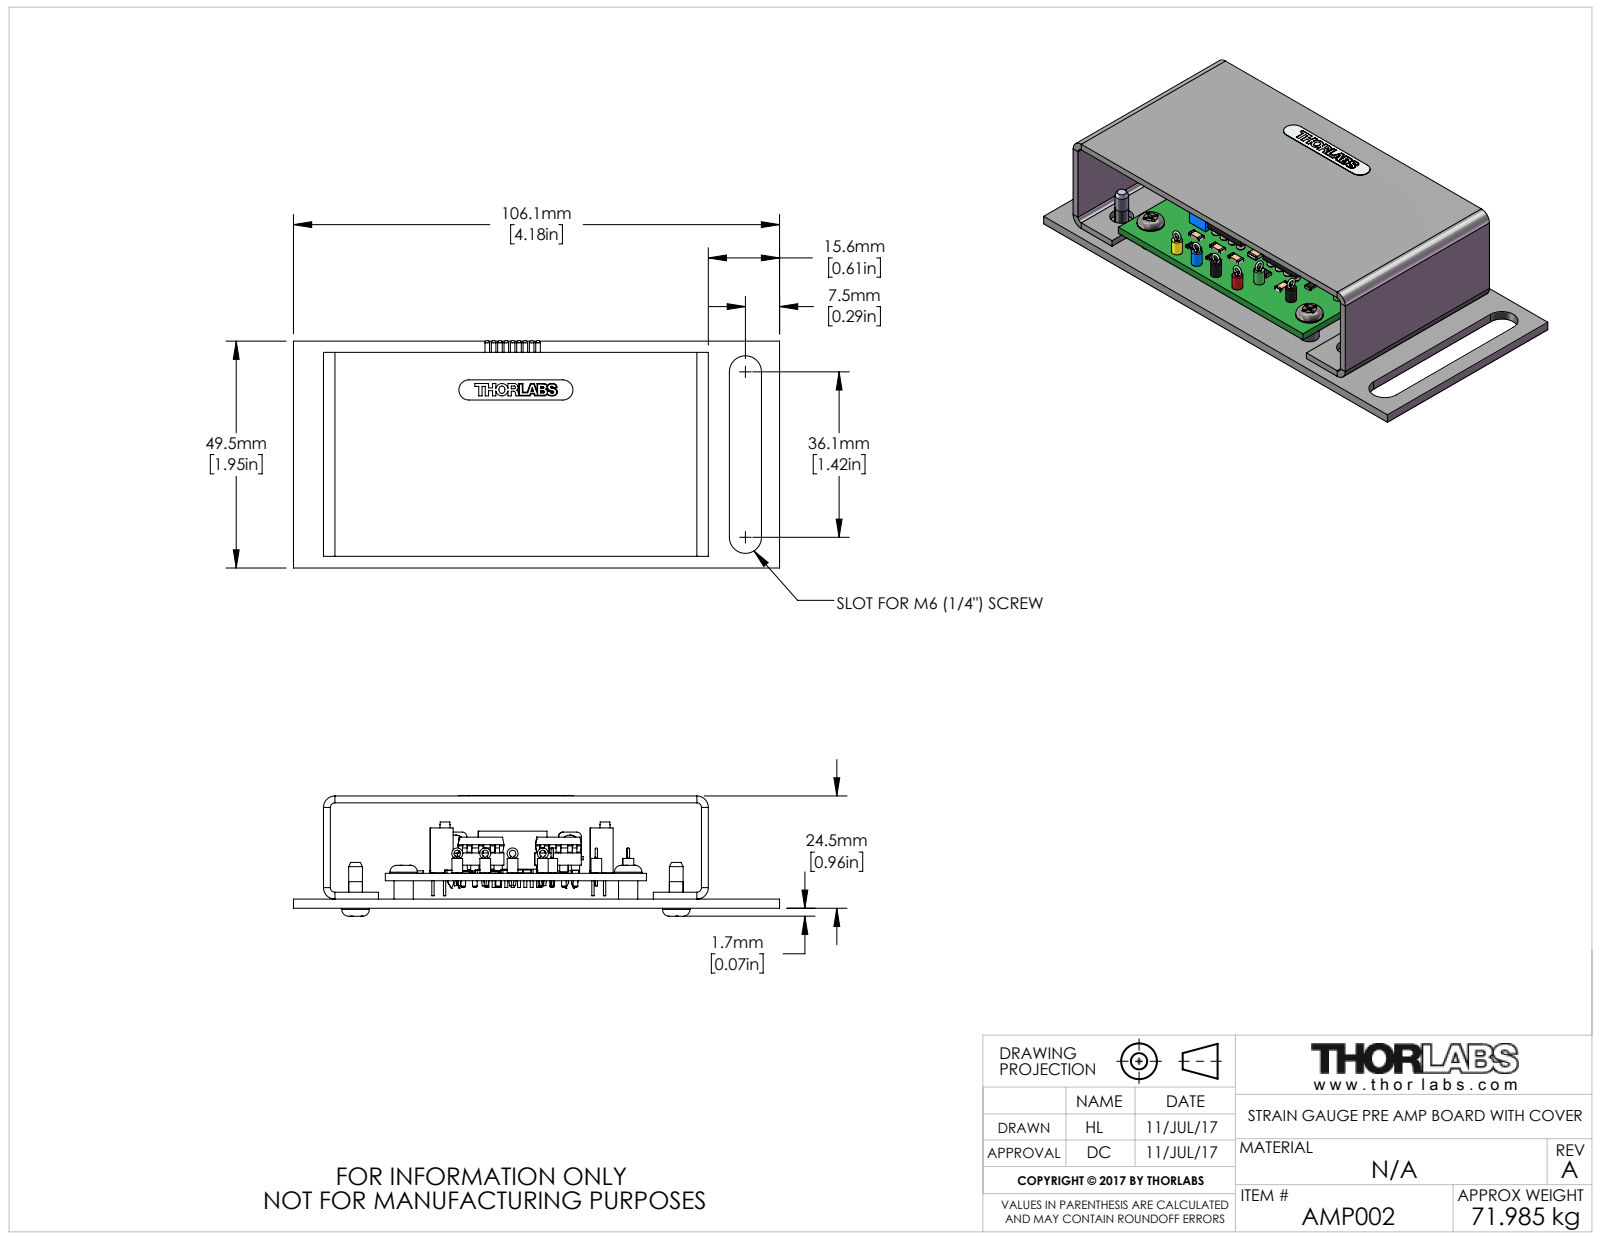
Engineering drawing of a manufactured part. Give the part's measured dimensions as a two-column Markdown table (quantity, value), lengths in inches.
| quantity | value |
| --- | --- |
| part name | AMP002 - Strain Gauge Pre Amp Board with Cover2 |
| STEP written by | SolidWorks 2016 (AUTOMOTIVE_DESIGN) |
| units | inches |
| bodies | 0 solids, 3076 faces (1830 planar, 795 cylindrical, 451 other) |
| overall size | 4.177 × 1.978 × 1.037 |
| round holes (diameter × count) | 0.031 × 21, 0.032 × 16, 0.071 × 16, 0.037 × 9, 0.04 × 8, 0.047 × 8, 0.035 × 6, 0.028 × 4, 0.098 × 4, 0.138 × 4, 0.165 × 4, 0.205 × 4 |
| round bosses / shafts (diameter × count) | 0.04 × 16, 0.039 × 9, 0.236 × 8, 0.118 × 8, 0.092 × 8, 0.02 × 6, 0.15 × 4, 0.138 × 2 |
| partial cylindrical surfaces (radius × count) | 0.039 × 20, 0.018 × 8, 0.098 × 8, 0.018 × 4, 0.028 × 4, 0.054 × 4, 0.067 × 4, 0.071 × 4 |
| main face-to-face distances | 0.059, 0.079, 0.827, 0.965, 0.886, 0.906, 0.665, 0.064, 0.236, 0.157 |
| hole center spacings | 0.124, 0.126, 0.109, 0.1, 0.198, 0.198, 0.2, 0.108 |
